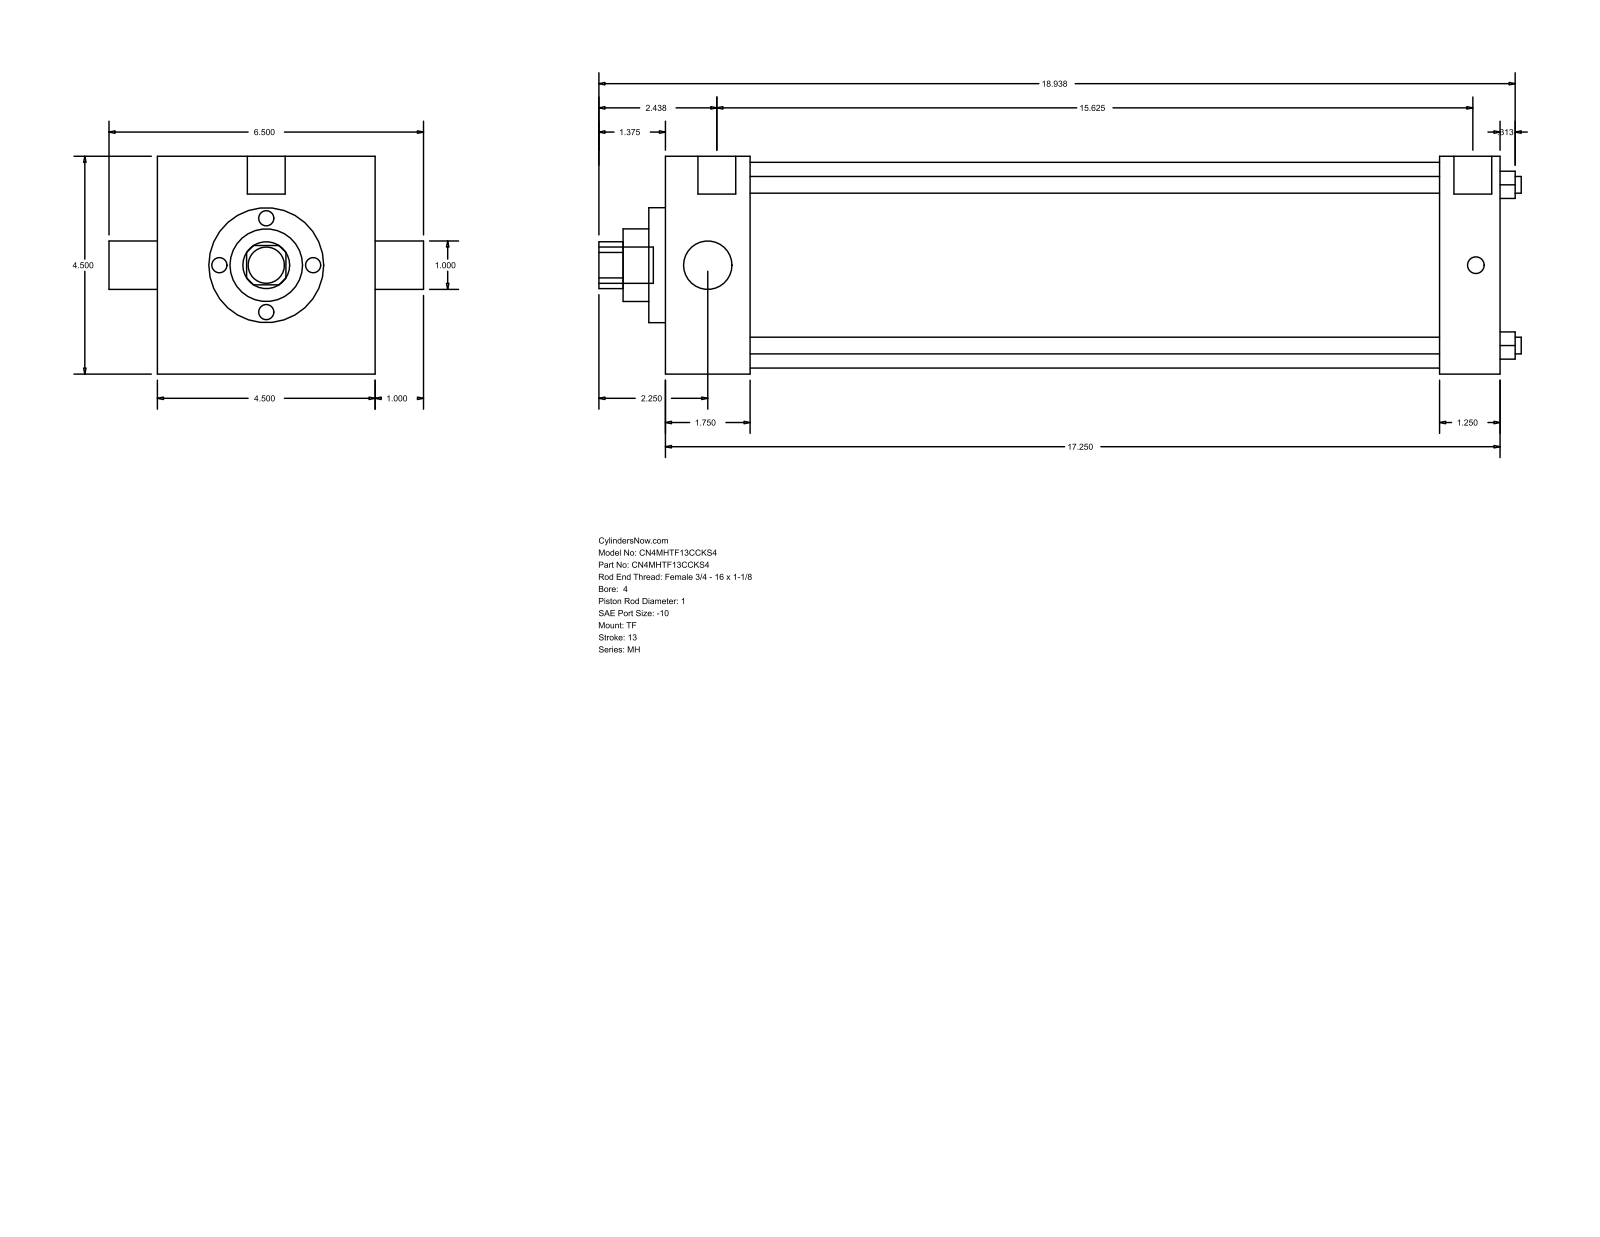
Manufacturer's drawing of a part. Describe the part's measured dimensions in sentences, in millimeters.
The part is named "MH_TF__0400_1". Its 3-D file was written by "GSSL Pune (CONFIG_CONTROL_DESIGN)". It is 0 solids with 86 faces: 61 planar, 25 cylindrical and 0 other. Overall it measures 484.19 by 165.1 by 114.3 millimeters. Round holes: 4 of diameter 8.76, 2 of diameter 25.4, 1 of diameter 38.1, 1 of diameter 60.33, 1 of diameter 107.95. Round bosses or shafts: 3 of diameter 8.73, 2 of diameter 19.84, 1 of diameter 19.05. Partial cylindrical surfaces (rounded edges, fillets, slot ends): 1 of radius 12.29. The main face-to-face distances are 114.3, 438.15, 44.46, 393.69, 406.4, 361.94, 31.75, 8.73, 53.19, 415.13. The hole center spacings are 59.62, 84.32, 119.25.
